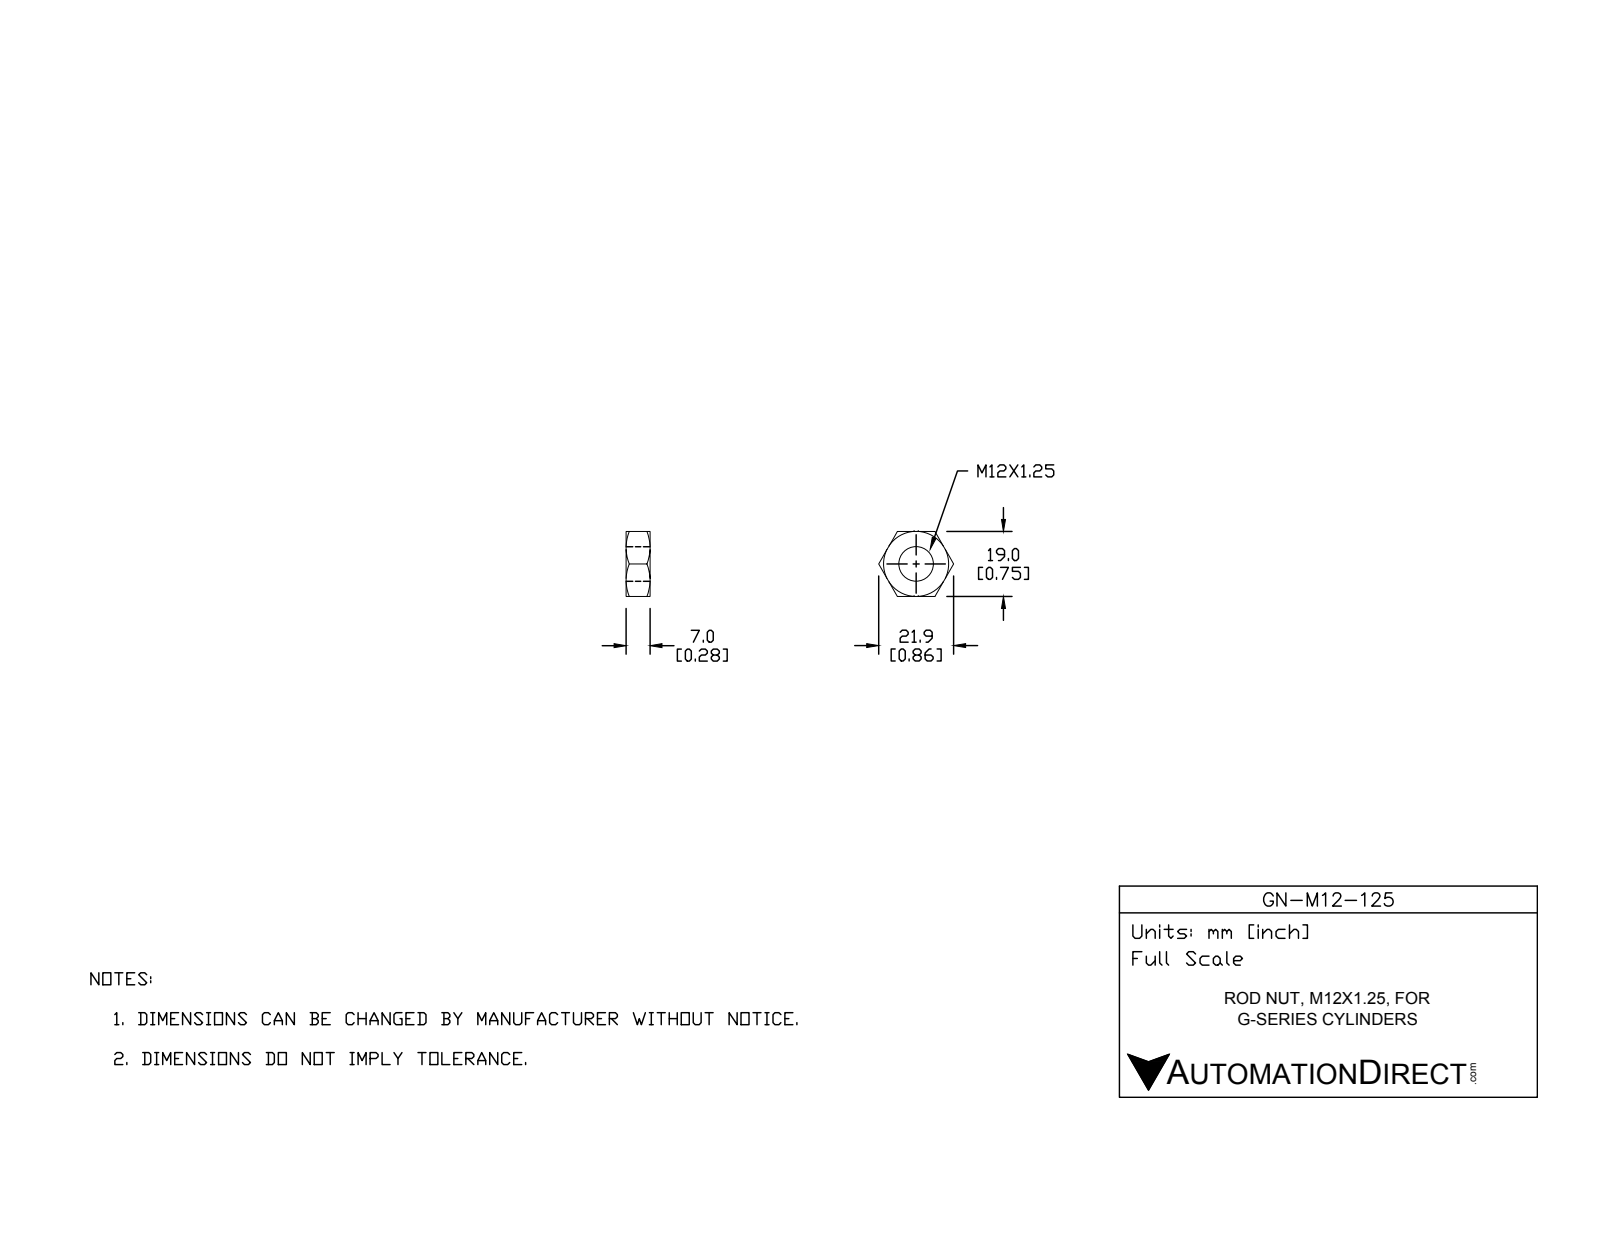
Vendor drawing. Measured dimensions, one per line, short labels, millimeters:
name: GN-M12-125
written by: SolidWorks 2017 (AUTOMOTIVE_DESIGN)
unit: mm
bodies: 1 solid, 24 faces (8 planar, 2 cylindrical, 14 other)
size: 21.94 × 19 × 7
volume: 1 521 mm³; area: 1 098 mm²
holes: 1× ⌀10.8
face distances: 19, 7
